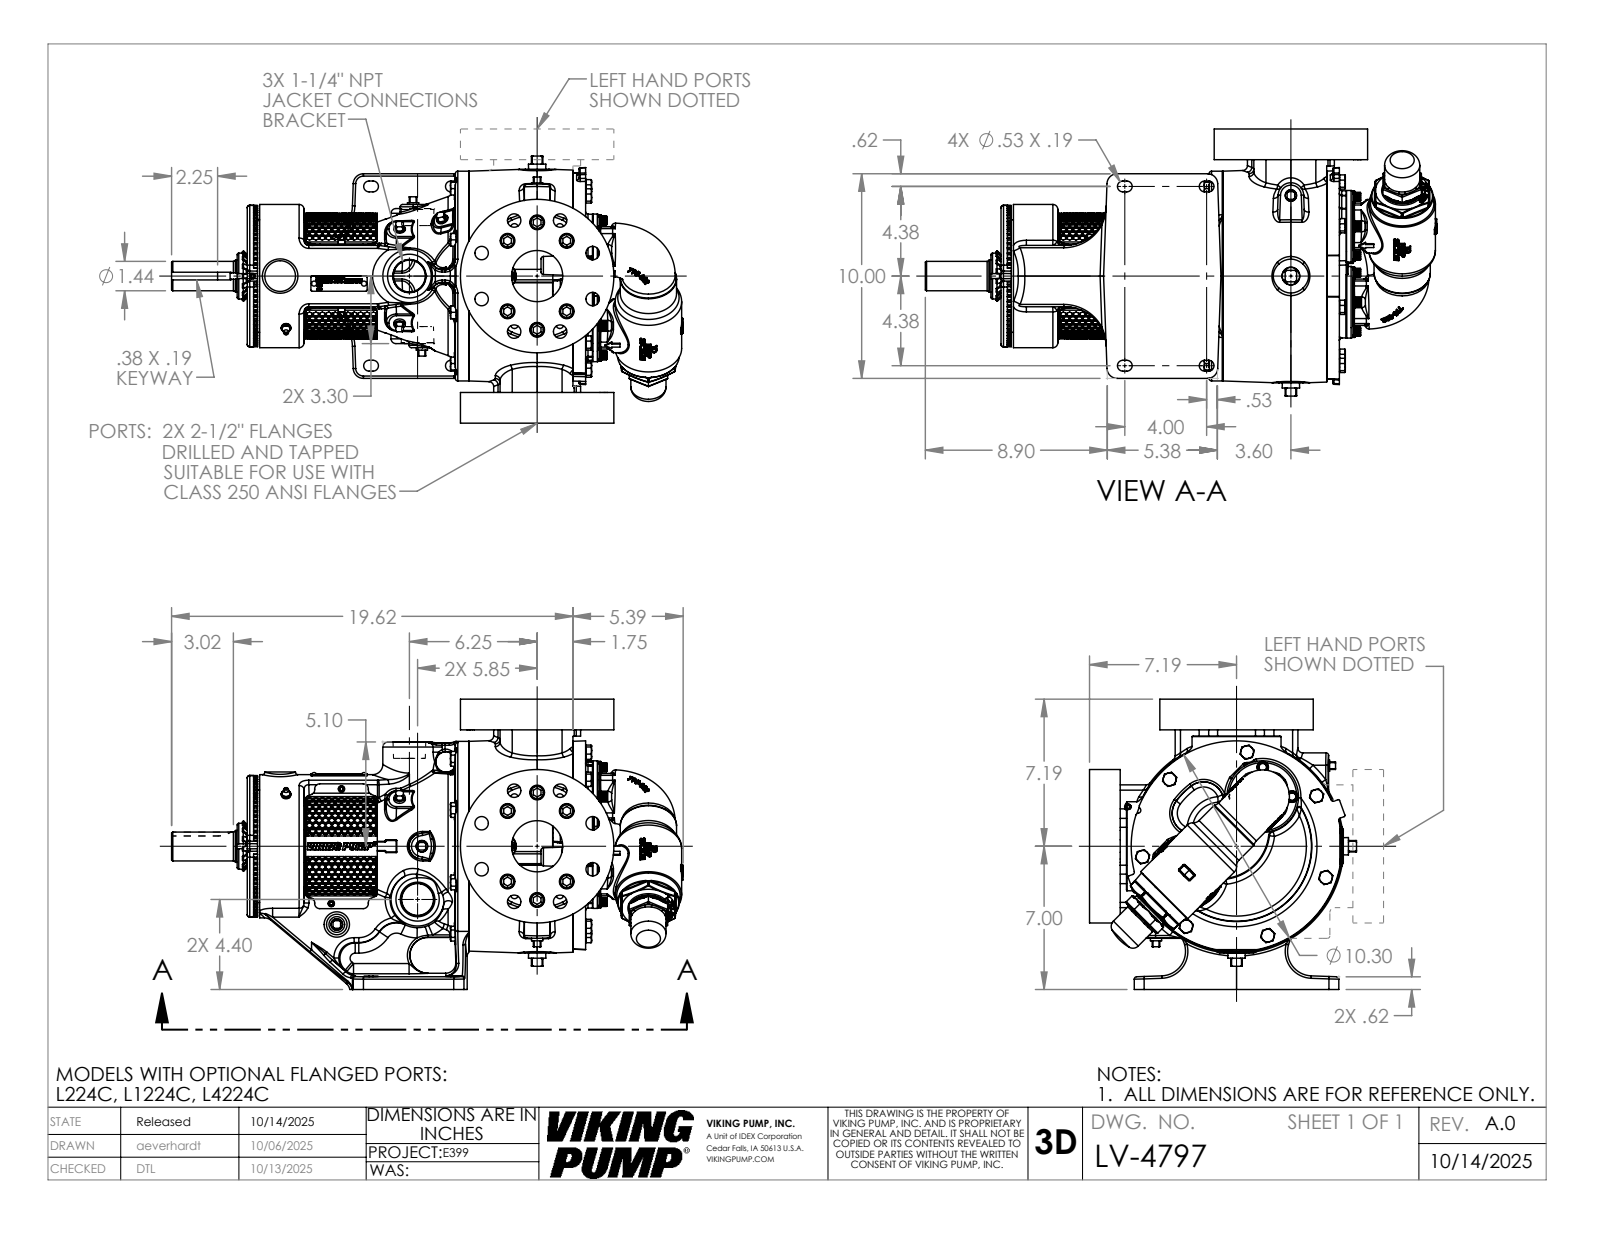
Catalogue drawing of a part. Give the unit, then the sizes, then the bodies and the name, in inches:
Units: inches
Overall size (bounding box): 25.01 × 14.188 × 13.053
Round holes (diameter × count): ⌀0.656 ×16, ⌀0.719 ×12, ⌀1.094 ×8, ⌀0.199 ×6, ⌀0.25 ×6, ⌀0.159 ×3, ⌀0.266 ×2, ⌀0.313 ×2, ⌀2.5 ×2, ⌀0.453 ×1, ⌀1.552 ×1, ⌀1.577 ×1
Round bosses / shafts (diameter × count): ⌀0.66 ×12, ⌀0.625 ×9, ⌀0.563 ×8, ⌀0.625 ×6, ⌀3.5 ×3, ⌀0.437 ×3, ⌀0.312 ×3, ⌀7.5 ×2
Partial cylindrical surfaces — rounded edges, fillets, slot ends (radius × count): R0.063 ×109, R0.069 ×74, R0.12 ×60, R0.03 ×36, R0.5 ×26, R0.24 ×16, R0.45 ×16, R1 ×16
Main face-to-face distances: 1.5, 14.187, 12.687, 13.792, 2.25, 3.537, 10.255, 2.75, 0.5, 2.143
Hole centre spacings: 2.248, 3, 2.937, 5.428, 1.375, 1.041, 1.402, 2.18
Volume: 1 108 in³ · Surface area: 1 524 in²
Bodies: 1 solid, 5647 faces (1906 planar, 1103 cylindrical, 2638 other)
Part name (STEP PRODUCT): LV-4797
STEP written by: SolidWorks 2024 (AUTOMOTIVE_DESIGN)
